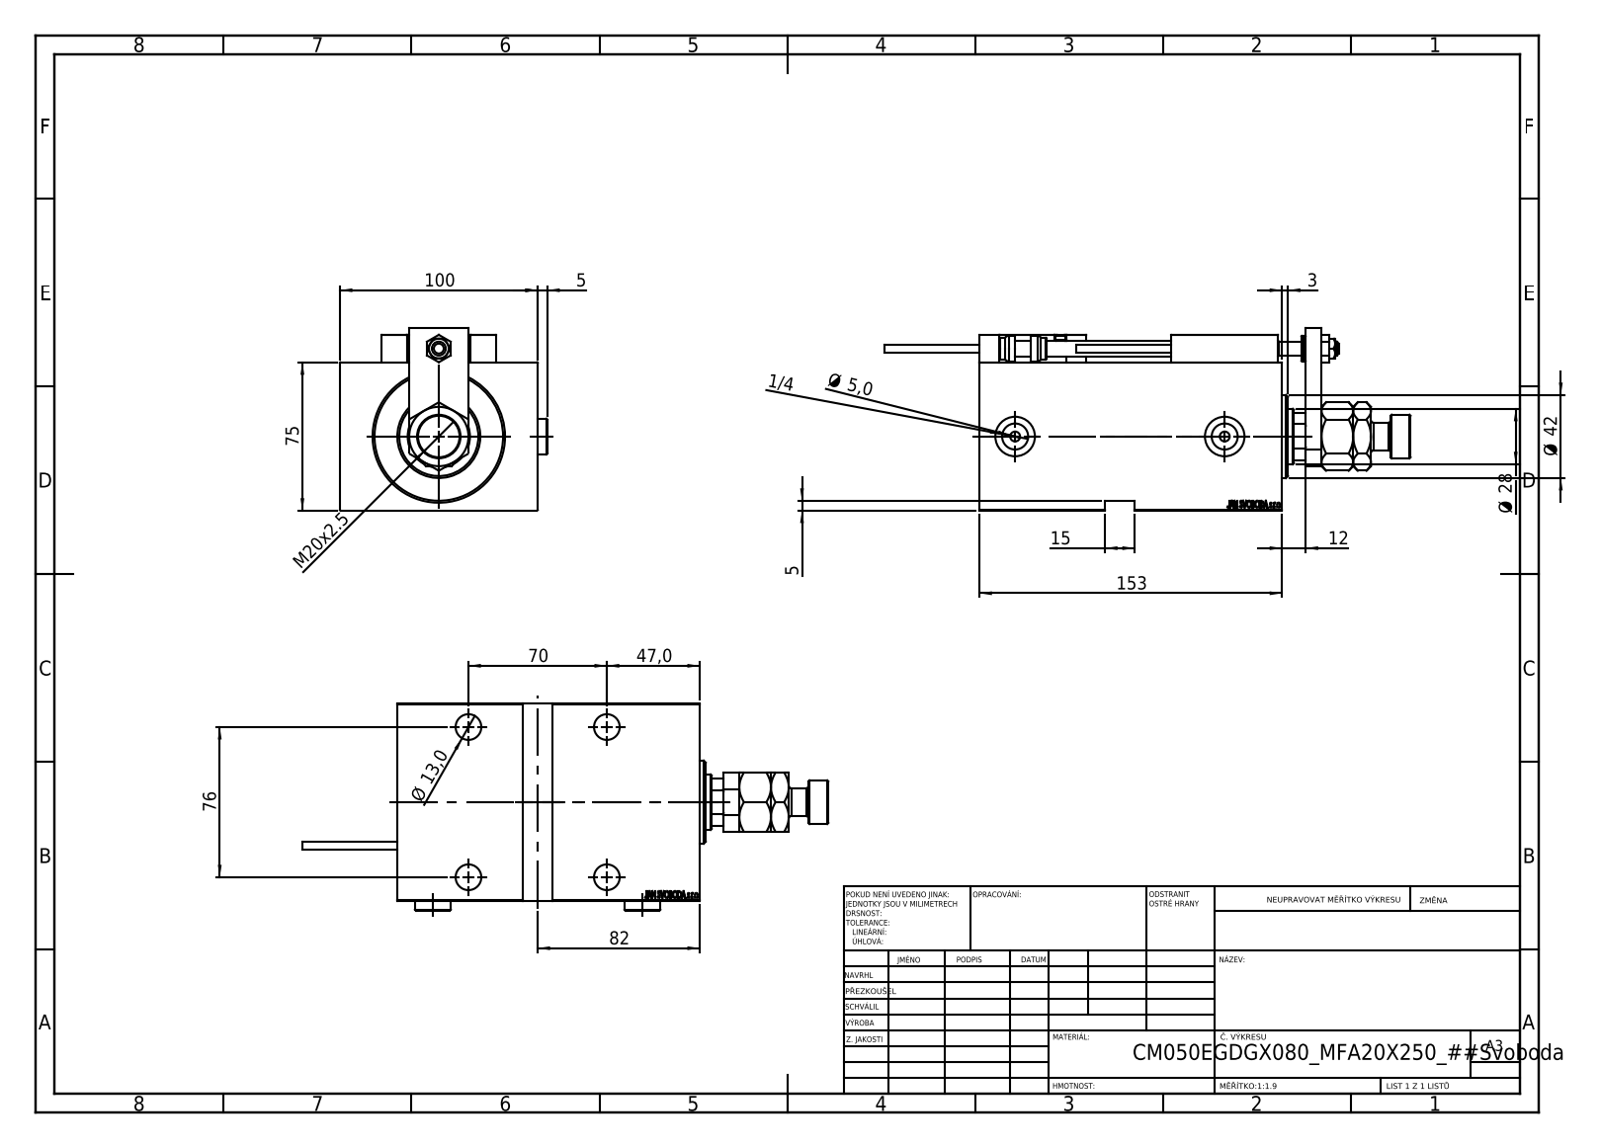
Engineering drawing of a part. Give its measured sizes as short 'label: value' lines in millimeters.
name: NUT_D10; ALLEN BOLT D8; NUT_D12; SWITCH_X_FRONT_BACK (+7 more)
written by: SolidWorks 2019 (CONFIG_CONTROL_DESIGN)
unit: mm
bodies: 27 solids, 1401 faces (622 planar, 202 cylindrical, 577 other)
size: 266 × 104.9 × 92.5
volume: 1 066 000 mm³; area: 174 827 mm²
holes: 5× ⌀8, 4× ⌀3.2, 4× ⌀4, 4× ⌀5, 4× ⌀13, 4× ⌀19, 3× ⌀20, 2× ⌀13.16, 1× ⌀7, 1× ⌀18.5, 1× ⌀28, 1× ⌀31.5
bosses: 2× ⌀18, 2× ⌀5, 2× ⌀3.8, 1× ⌀52, 1× ⌀42, 1× ⌀22, 1× ⌀14, 1× ⌀13
rounds: 30× R0.3, 2× R3, 1× R13.5
face distances: 75, 100, 14, 153, 5, 139, 25, 20, 8, 12
hole spacings: 11.37, 20, 29.59, 29.69, 36.06, 41.77, 42.19, 48.83
